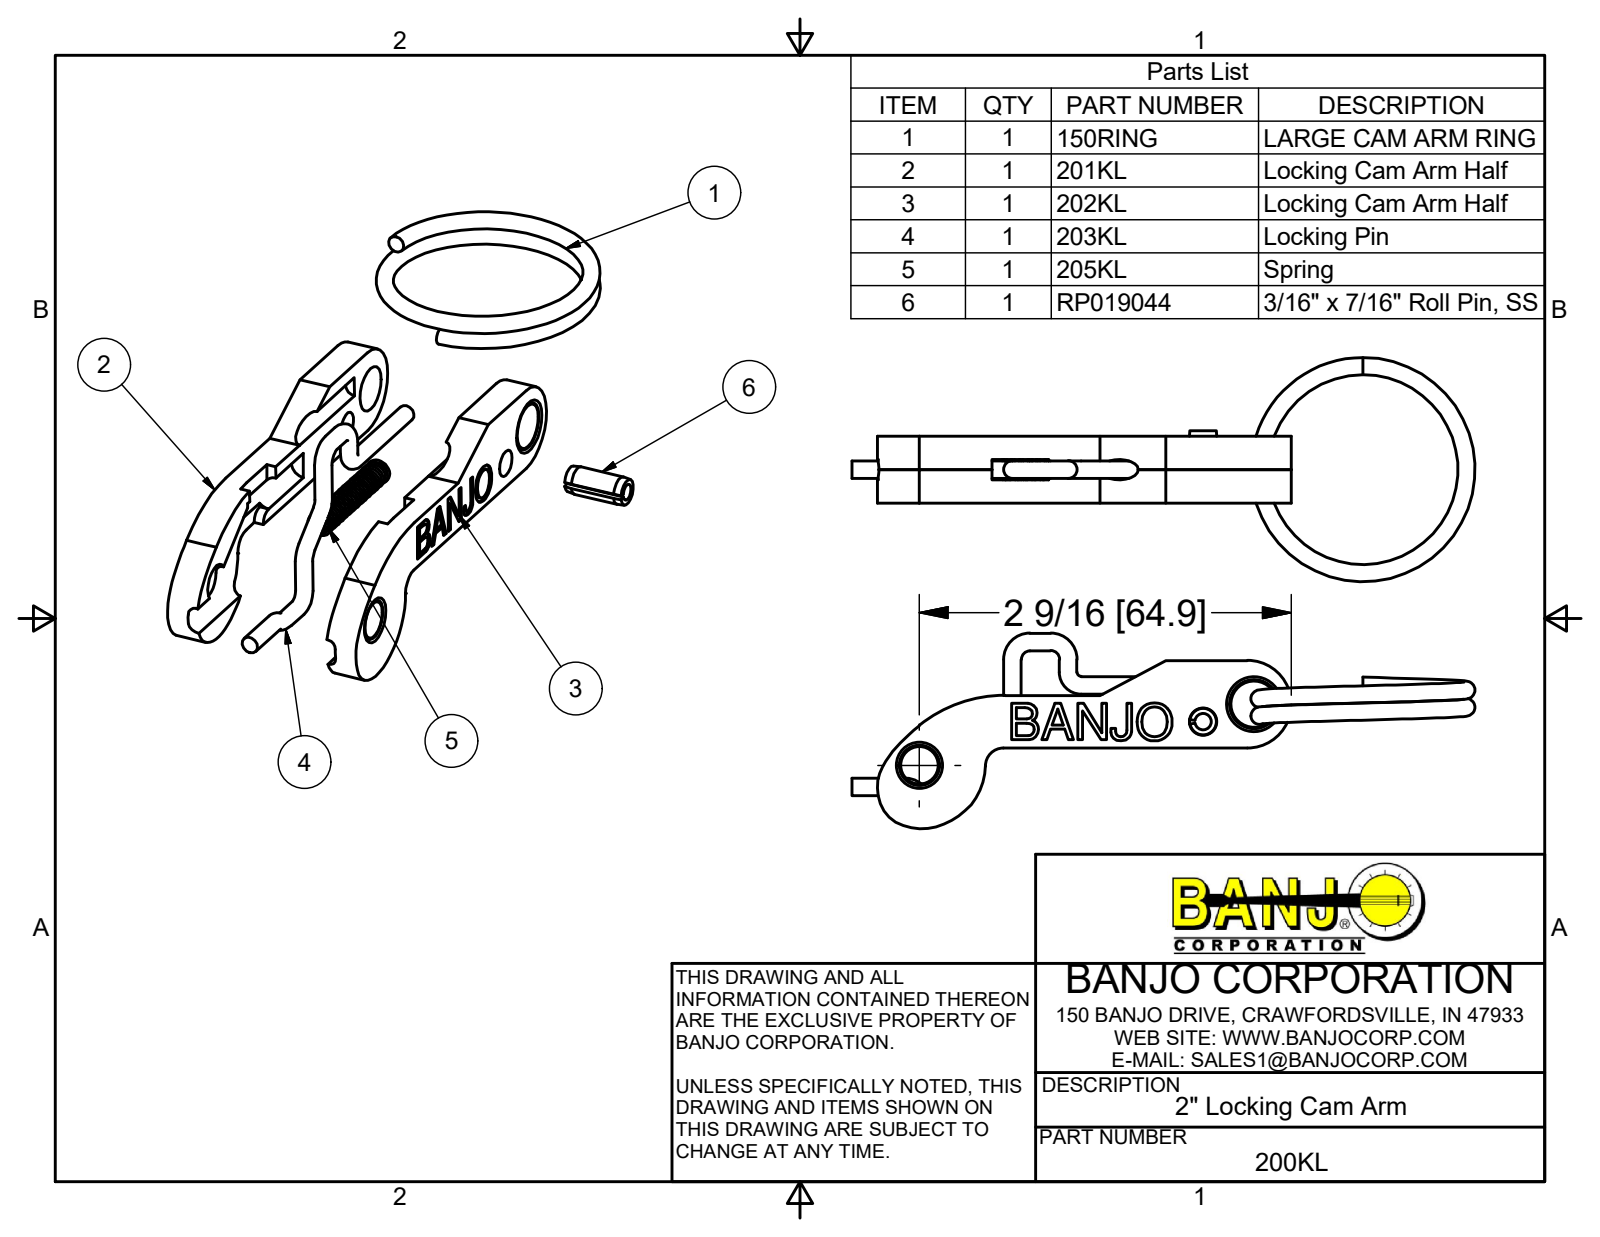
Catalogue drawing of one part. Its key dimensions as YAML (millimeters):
part_name: "200KL; 201KL; 202KL; 205KL (+3 more)"
step_written_by: "Autodesk Inventor 2017 (AUTOMOTIVE_DESIGN)"
units: millimeters
bodies: {solids: 6, faces: 266, planar: 143, cylindrical: 35, other: 88}
overall_size: [108.83, 39.14, 34.13]
volume: 10795
surface_area: 9585
round_holes:
  - {diameter: 2.9, count: 1}
  - {diameter: 3.56, count: 1}
  - {diameter: 4.75, count: 1}
  - {diameter: 4.83, count: 1}
  - {diameter: 6.55, count: 1}
  - {diameter: 8, count: 1}
round_bosses_or_shafts:
  - {diameter: 3.05, count: 9}
  - {diameter: 4.93, count: 1}
partial_cylinders:
  - {radius: 1.4, count: 2}
  - {radius: 1.78, count: 2}
  - {radius: 2.03, count: 1}
  - {radius: 3.15, count: 1}
  - {radius: 7.64, count: 1}
  - {radius: 23.88, count: 1}
face_to_face_distances: [5.84, 11.68, 4.06, 7.62, 1.78, 9.17, 15.29, 6.12, 3.56, 11.43]
hole_center_spacings: [6.4, 9.4, 50.11, 59.39]
